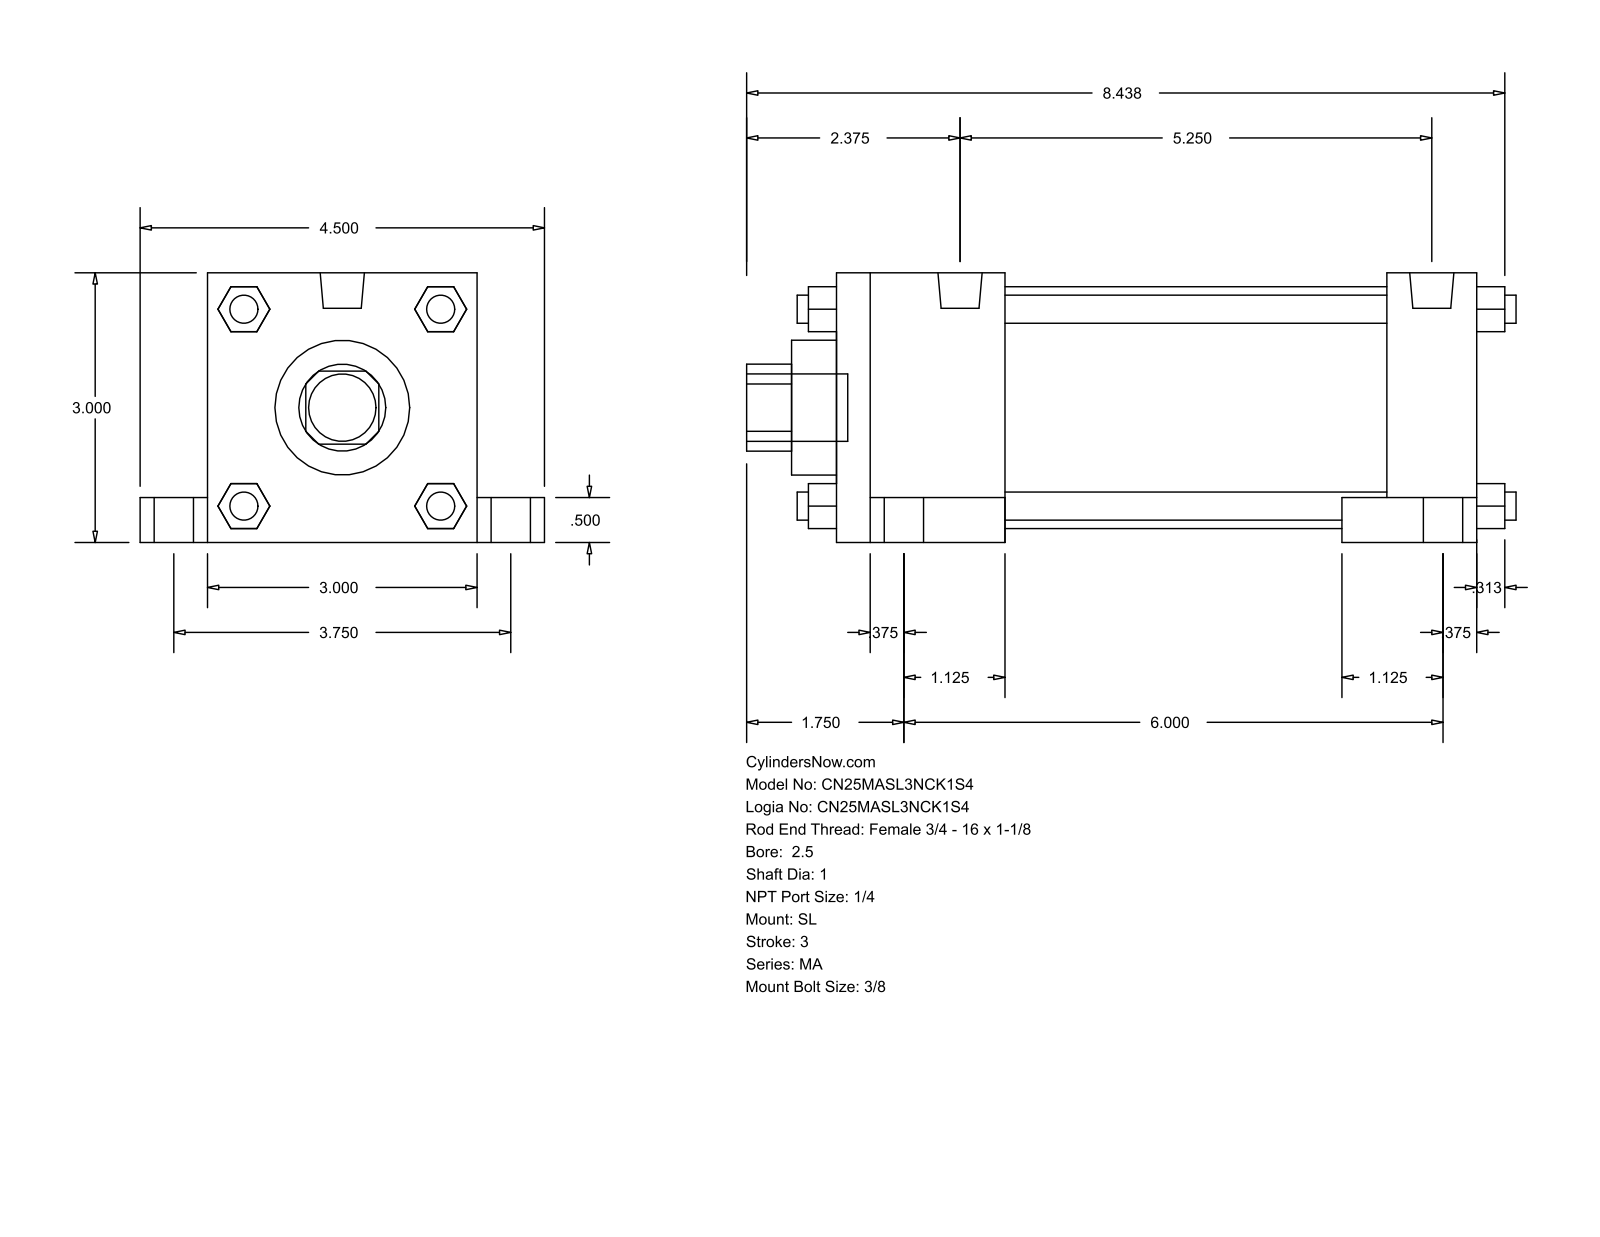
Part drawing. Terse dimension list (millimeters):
name: MA_SL__0250_1
written by: GSSL Pune (CONFIG_CONTROL_DESIGN)
unit: mm
bodies: 0 solids, 148 faces (112 planar, 36 cylindrical, 0 other)
size: 217.49 × 114.3 × 76.2
holes: 1× ⌀25.4, 1× ⌀38.1, 1× ⌀68.33
bosses: 8× ⌀7.94, 4× ⌀17.46, 4× ⌀11.11, 2× ⌀12.49, 1× ⌀19.05
rounds: 1× R12.29
face distances: 76.2, 180.98, 12.7, 47.63, 133.35, 155.57, 107.94, 25.41, 19.05, 95.25
